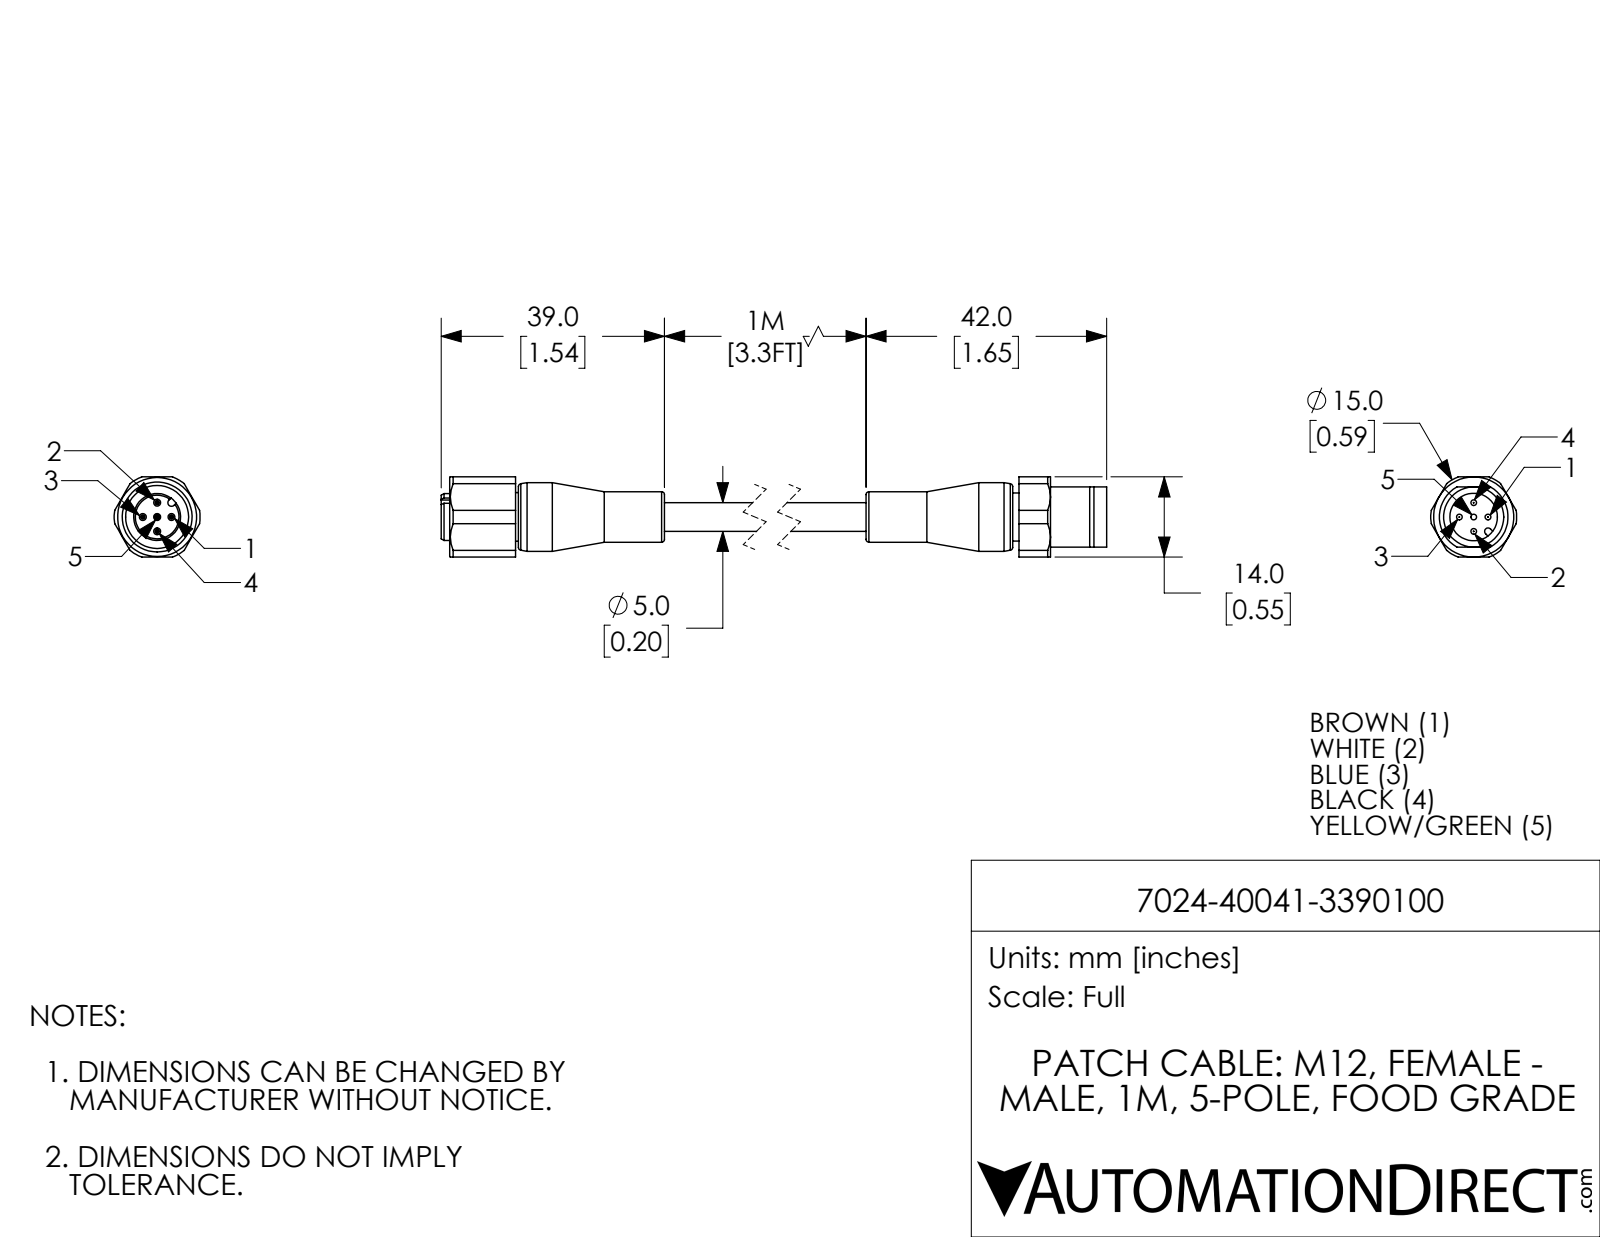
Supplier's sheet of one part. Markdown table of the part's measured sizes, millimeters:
| quantity | value |
| --- | --- |
| part name | 7024-40041-3390100; 7024-40041-3390100_FEMALE; 7024-40041-3390100_MALE |
| STEP written by | SolidWorks 2018 (AUTOMOTIVE_DESIGN) |
| units | millimeters |
| bodies | 2 solids, 148 faces (43 planar, 62 cylindrical, 43 other) |
| overall size | 131.2 × 15 × 14 |
| volume | 8 050 mm³ |
| surface area | 5 092 mm² |
| round holes (diameter × count) | 1.2 × 5, 8.3 × 1, 11 × 1 |
| round bosses / shafts (diameter × count) | 1 × 5, 12 × 1, 10.5 × 1, 8.8 × 1, 8.5 × 1, 8.4 × 1, 8.2 × 1, 5 × 1 |
| partial cylindrical surfaces (radius × count) | 0.6 × 1, 0.7 × 1, 7.5 × 1 |
| main face-to-face distances | 14, 102.9, 1.8, 12.2, 113.3, 7.5, 5.5, 109.3, 6.4, 108.4 |
| hole center spacings | 2.5, 3.5, 5 |
